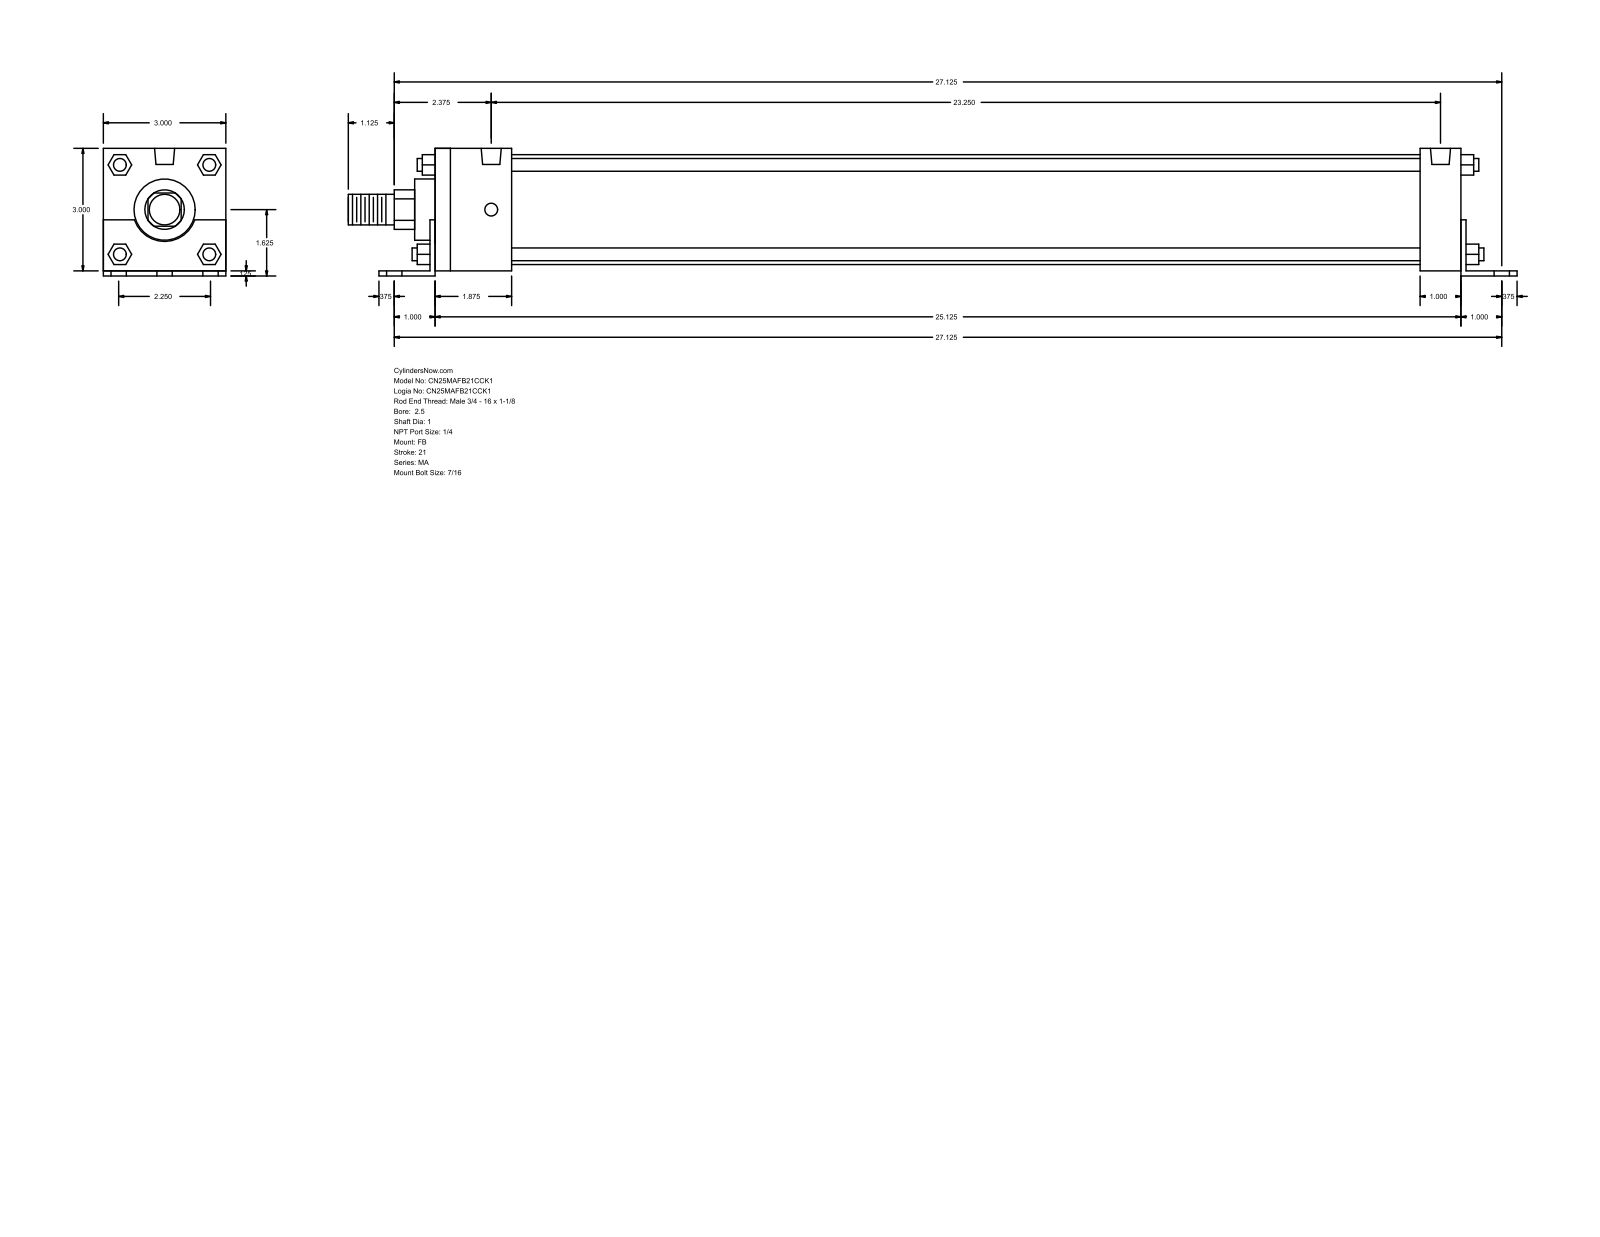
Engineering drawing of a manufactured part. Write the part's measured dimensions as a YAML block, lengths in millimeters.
part_name: "MA_FB__0250_1"
step_written_by: "GSSL Pune (CONFIG_CONTROL_DESIGN)"
units: millimeters
bodies: {solids: 0, faces: 140, planar: 105, cylindrical: 35, other: 0}
overall_size: [727.08, 79.38, 76.2]
round_holes:
  - {diameter: 11.11, count: 6}
  - {diameter: 7.94, count: 4}
  - {diameter: 12.49, count: 2}
round_bosses_or_shafts:
  - {diameter: 7.94, count: 4}
  - {diameter: 68.33, count: 1}
  - {diameter: 38.1, count: 1}
  - {diameter: 25.4, count: 1}
  - {diameter: 19.05, count: 1}
partial_cylinders:
  - {radius: 12.29, count: 1}
  - {radius: 19.81, count: 1}
face_to_face_distances: [76.2, 3.17, 79.37, 641.35, 638.18, 12.7, 50.8, 47.63, 590.55, 593.72]
hole_center_spacings: [28.57, 689.57, 688.98, 47.62, 57.14, 66.75, 590.55, 629.3]
